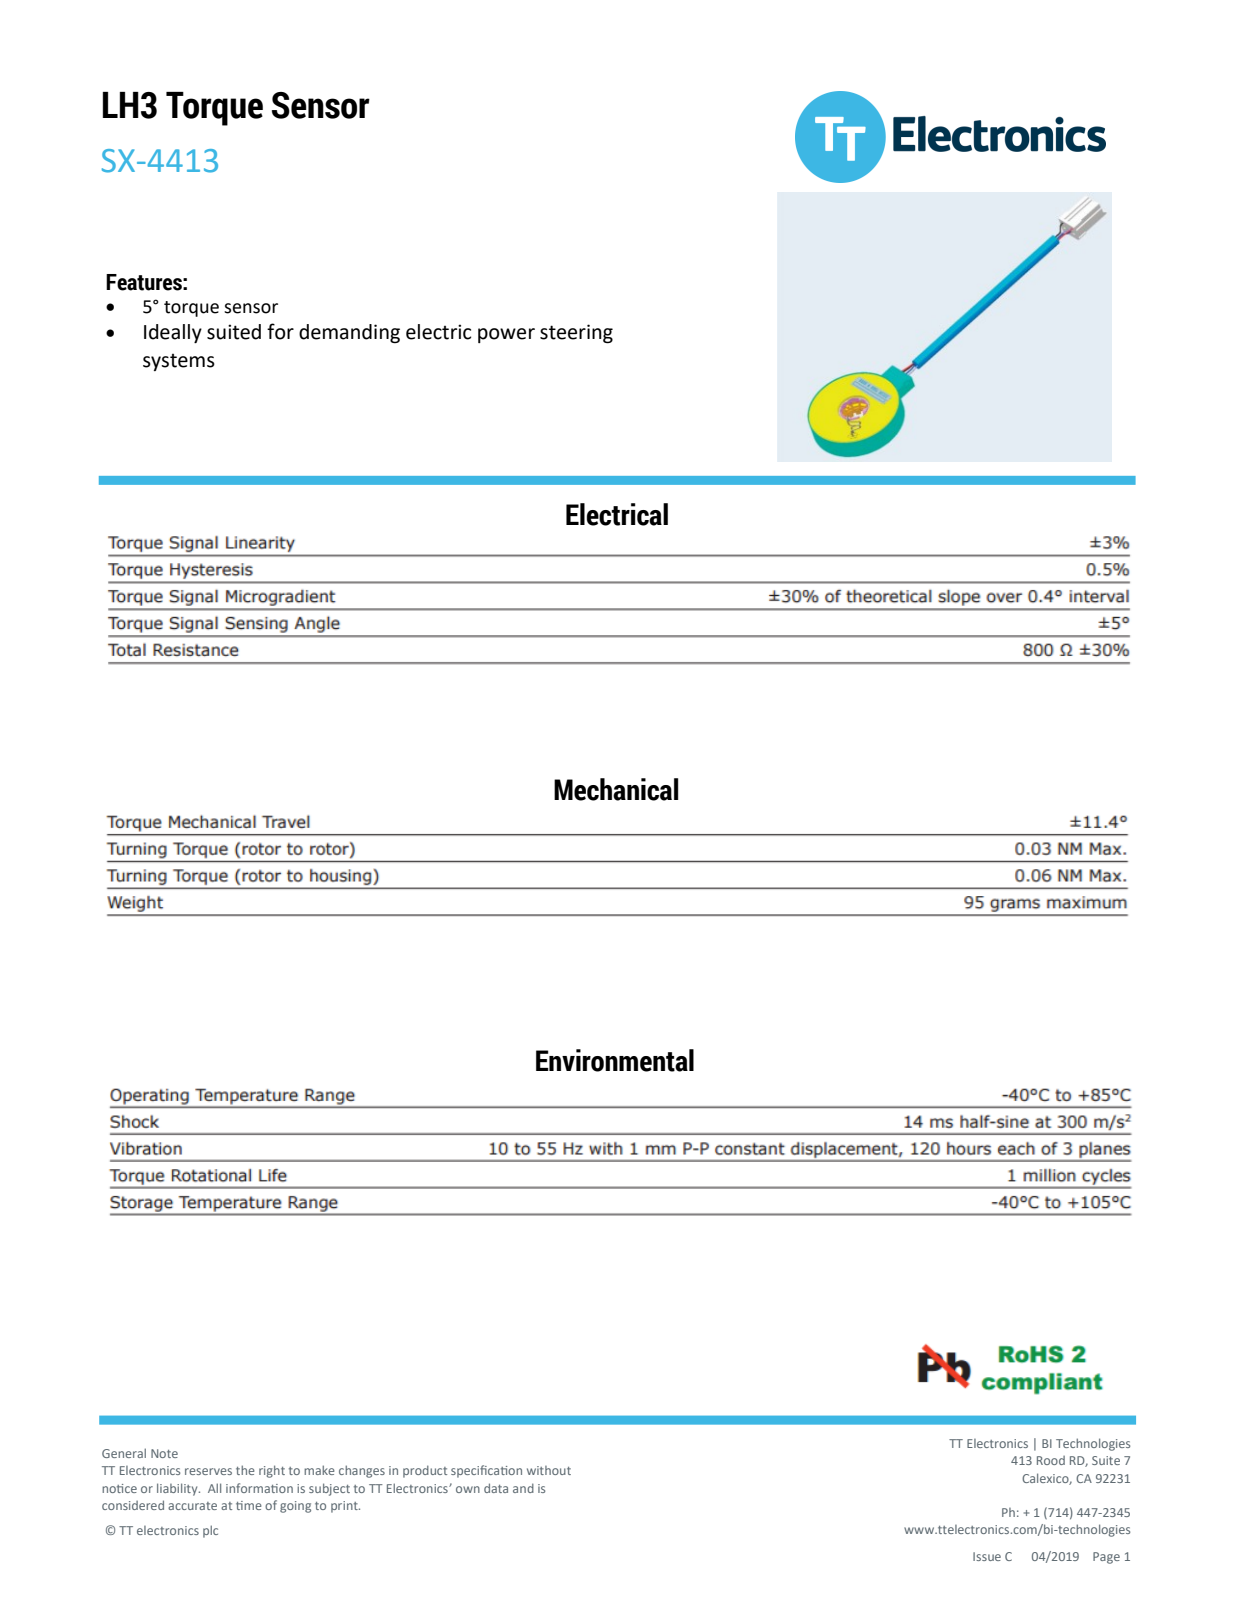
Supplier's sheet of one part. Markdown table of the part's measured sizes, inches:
| quantity | value |
| --- | --- |
| part name | SX-4413A_SW0009 |
| STEP written by | CREO PARAMETRIC BY PTC INC, 2014500 (CONFIG_CONTROL_DESIGN) |
| units | inches |
| bodies | 3 solids, 2173 faces (1121 planar, 735 cylindrical, 317 other) |
| overall size | 13.214 × 3.2 × 1.835 |
| volume | 5.851 in³ |
| surface area | 66.68 in² |
| round holes (diameter × count) | 0.02 × 4, 0.04 × 4, 0.985 × 1, 1.046 × 1, 1.126 × 1, 1.146 × 1, 1.241 × 1, 1.247 × 1, 1.255 × 1, 1.345 × 1, 2.57 × 1 |
| round bosses / shafts (diameter × count) | 0.062 × 12, 0.025 × 8, 0.047 × 6, 0.094 × 4, 0.064 × 4, 3.2 × 1, 1.24 × 1, 1.234 × 1 |
| partial cylindrical surfaces (radius × count) | 0.007 × 72, 0.012 × 72, 0.01 × 46, 0.005 × 44, 0.006 × 42, 0.02 × 29, 0.016 × 19, 0.028 × 18 |
| main face-to-face distances | 0.719, 0.05, 0.055, 0.669, 0.664, 0.06, 0.808, 0.521, 0.13, 0.144 |
| hole center spacings | 0.115, 0.345, 0.23, 0.46, 1.72, 1.723, 1.737, 1.756 |
